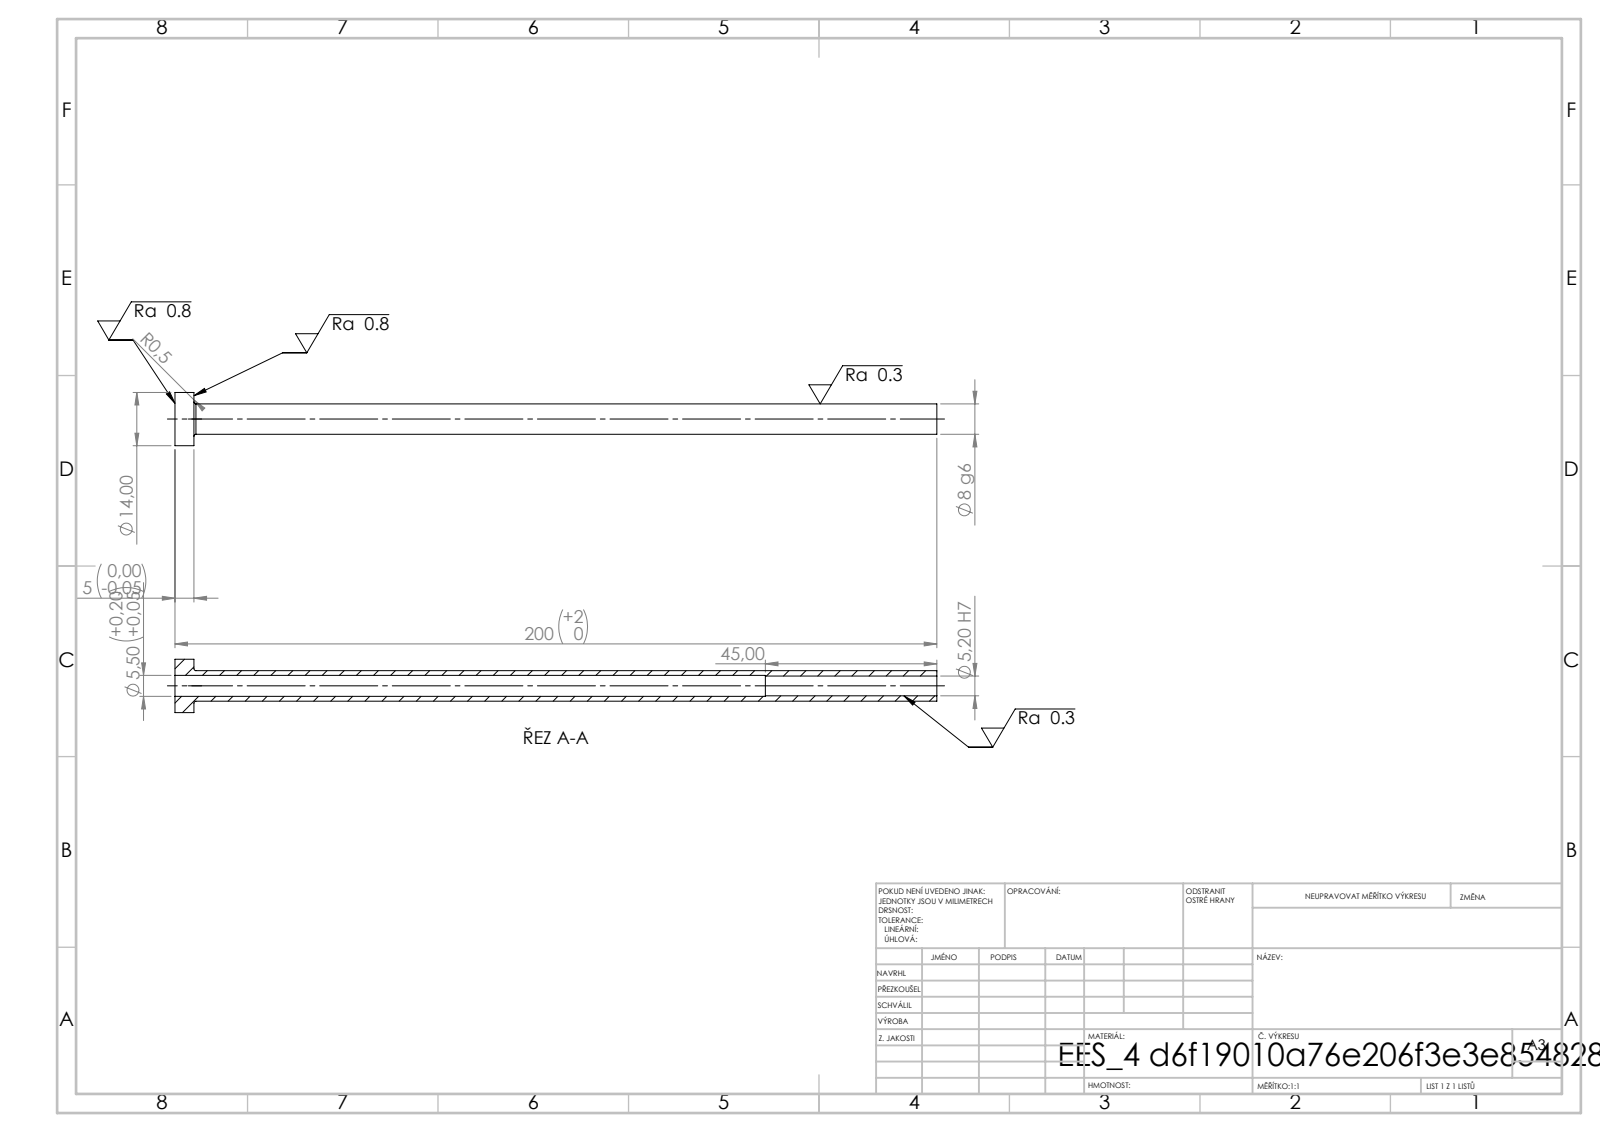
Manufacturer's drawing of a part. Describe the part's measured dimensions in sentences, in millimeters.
Its 3-D file was written by "SolidWorks 2019 (CONFIG_CONTROL_DESIGN)". It is 1 solid with 14 faces: 4 planar, 8 cylindrical and 2 other. Overall it measures 200 by 14 by 14 millimeters. Its volume is 5 935 cubic millimeters and its surface area 8 794 square millimeters. Round holes: 1 of diameter 5.2, 1 of diameter 5.5. Round bosses or shafts: 1 of diameter 14, 1 of diameter 8. The main face-to-face distances are 5, 200, 195, 155, 150, 45.
